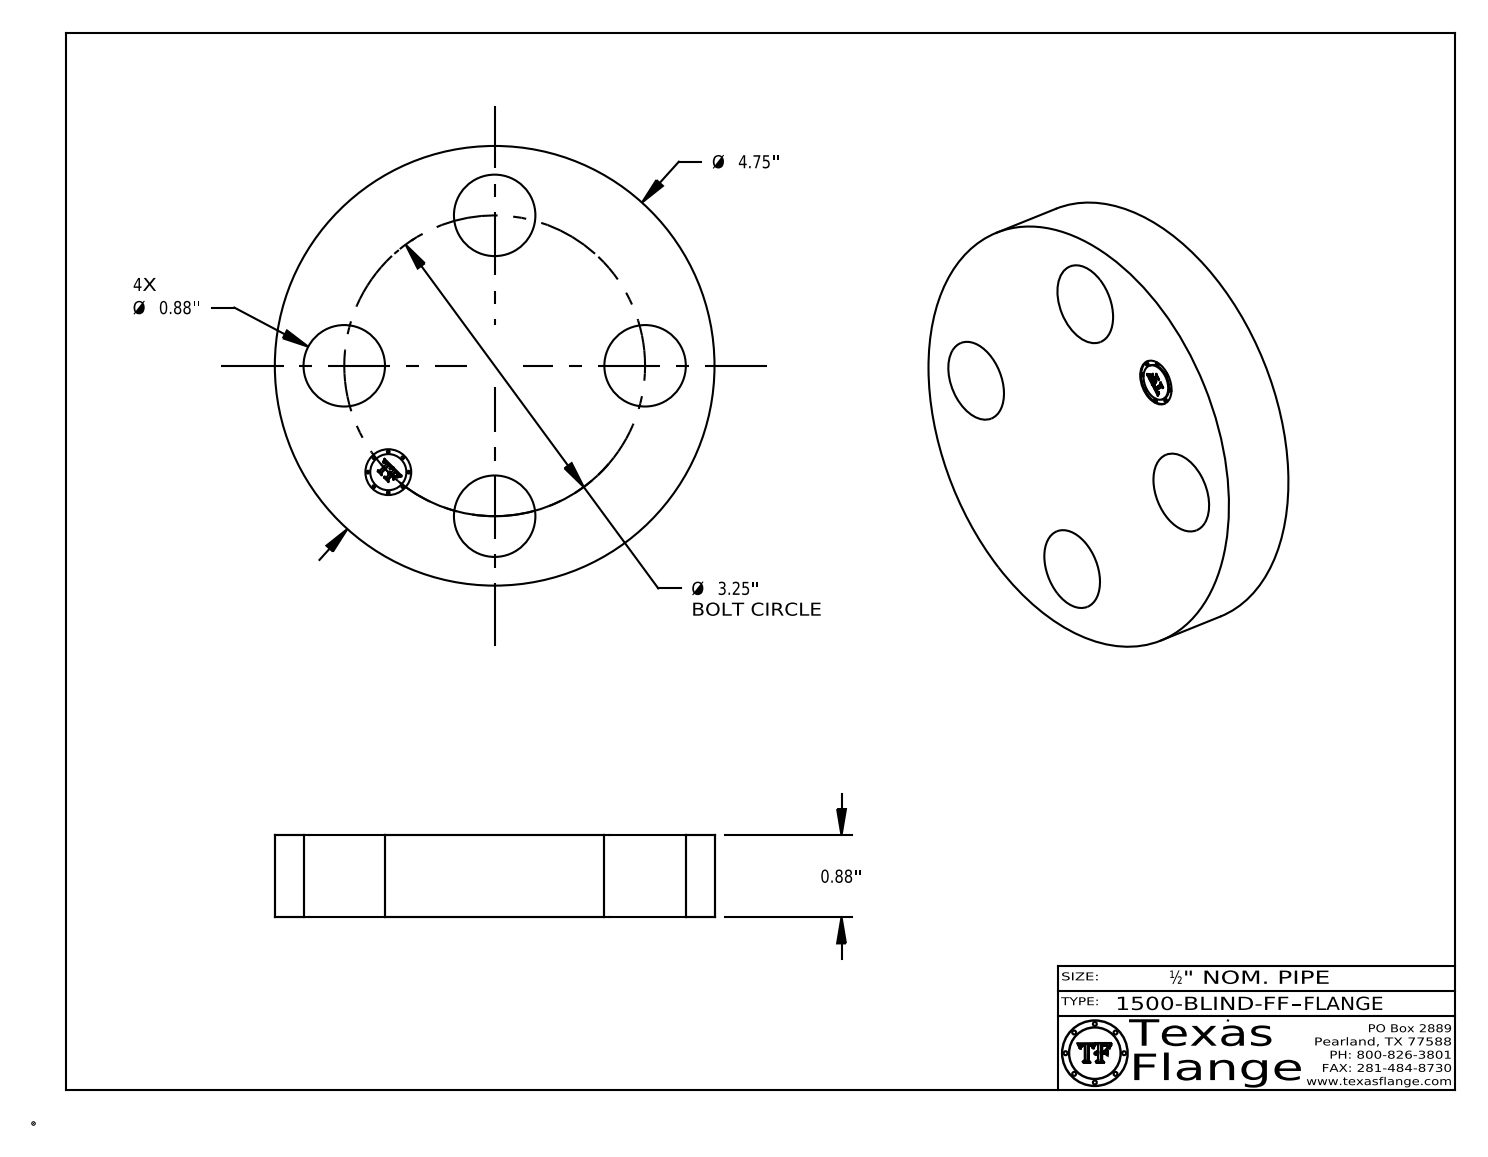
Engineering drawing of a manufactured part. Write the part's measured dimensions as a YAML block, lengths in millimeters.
part_name: "1500-BLIND-FF"
step_written_by: "CATIA V5 STEP AP214 (AUTOMOTIVE_DESIGN)"
units: millimeters
bodies: {solids: 1, faces: 397, planar: 367, cylindrical: 30, other: 0}
overall_size: [120.7, 120.7, 22.4]
volume: 220400
surface_area: 34540
round_holes:
  - {diameter: 22.4, count: 4}
  - {diameter: 12.6, count: 1}
round_bosses_or_shafts:
  - {diameter: 0.8, count: 8}
  - {diameter: 120.7, count: 1}
  - {diameter: 9.9, count: 1}
face_to_face_distances: [22.4, 22, 0.4, 3.8, 3.7, 0.7, 2.4, 3.1, 0.5, 1.9]
hole_center_spacings: [58.4, 31.6, 76.3, 82.6]
